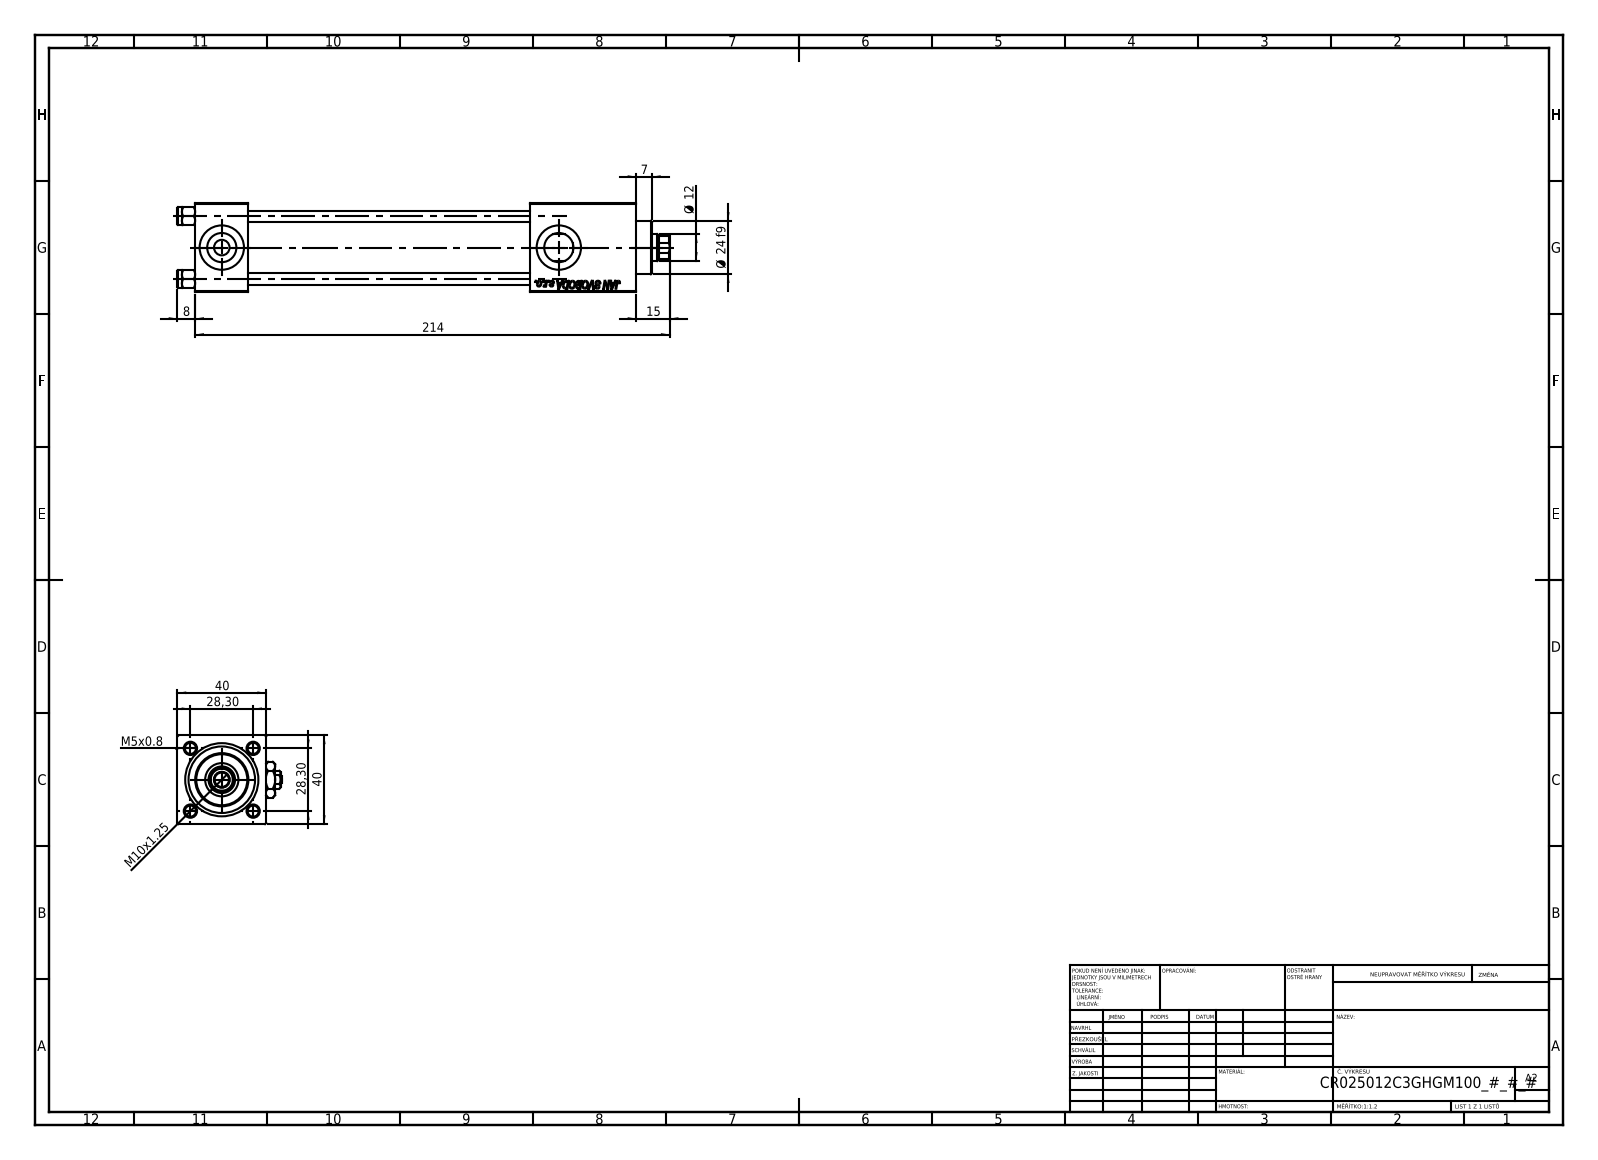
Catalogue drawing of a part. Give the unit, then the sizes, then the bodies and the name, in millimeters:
Units: millimetres
Overall size (bounding box): 222 × 47 × 40
Round holes (diameter × count): ⌀5 ×4, ⌀20 ×3, ⌀7 ×2, ⌀13.16 ×2, ⌀6.5 ×1, ⌀12 ×1, ⌀15 ×1, ⌀25 ×1, ⌀30 ×1
Round bosses / shafts (diameter × count): ⌀8 ×4, ⌀31 ×1, ⌀24 ×1
Partial cylindrical surfaces — rounded edges, fillets, slot ends (radius × count): R5.5 ×1
Main face-to-face distances: 40, 24, 39.8, 170.3, 146.3, 48, 151, 127, 19.3, 199
Hole centre spacings: 20.01, 28.3, 40.02, 152
Volume: 177 428 mm³ · Surface area: 78 326 mm²
Bodies: 13 solids, 1248 faces (572 planar, 98 cylindrical, 578 other)
Part name (STEP PRODUCT): V215_VC_A; NUT_M5_C; V215CR_VCP_C; Zatka_pro_OIL_PORT (+2 more)
STEP written by: SolidWorks 2019 (CONFIG_CONTROL_DESIGN)
